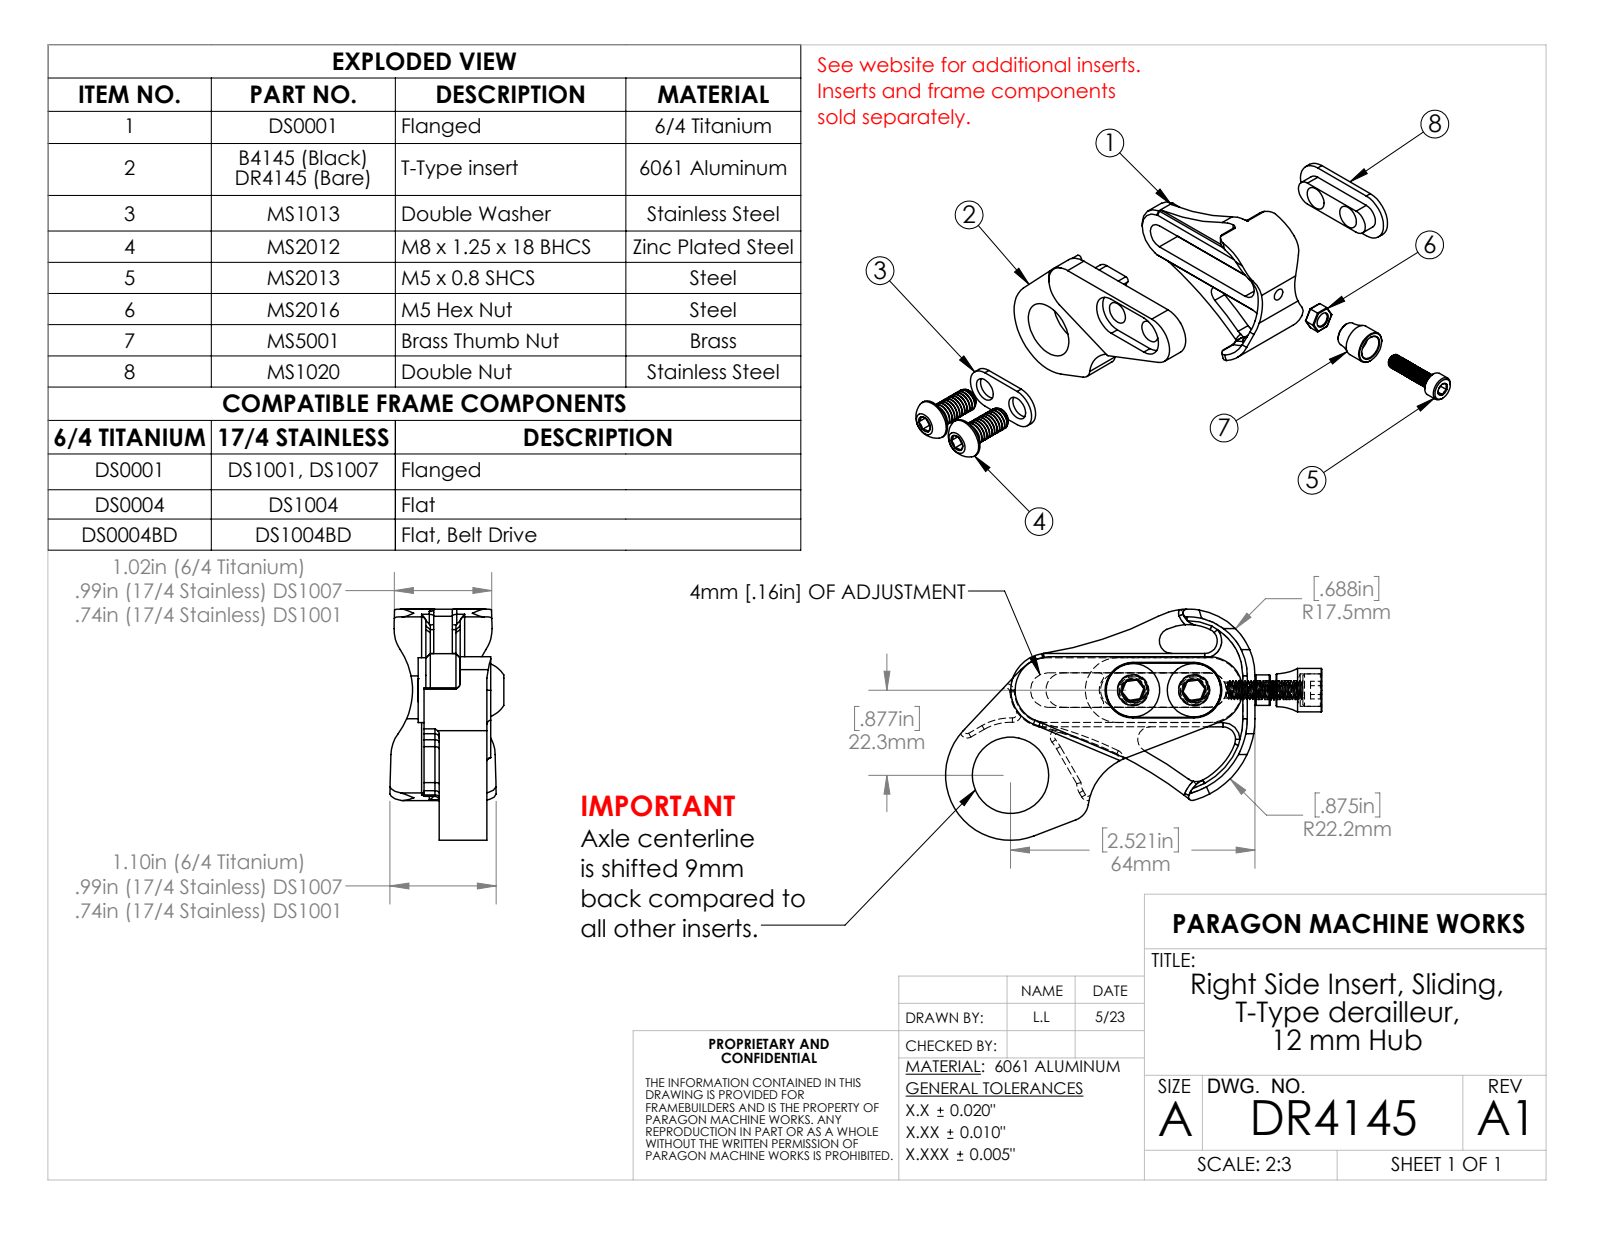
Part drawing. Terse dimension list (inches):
name: DR4145
written by: SolidWorks 2022 (AUTOMOTIVE_DESIGN)
unit: in
bodies: 1 solid, 79 faces (21 planar, 41 cylindrical, 17 other)
size: 2.816 × 2.326 × 0.688
volume: 1.213 in³; area: 12.86 in²
holes: 2× ⌀0.312, 1× ⌀0.787
rounds: 11× R0.045, 3× R0.178, 2× R0.03, 2× R0.287, 1× R0.157, 1× R0.2, 1× R0.345, 1× R0.39
face distances: 0.315, 0.275, 0.04, 0.216, 0.491, 0.531, 0.118, 0.197, 0.413, 0.078
hole spacings: 0.63, 1.537, 2.085
